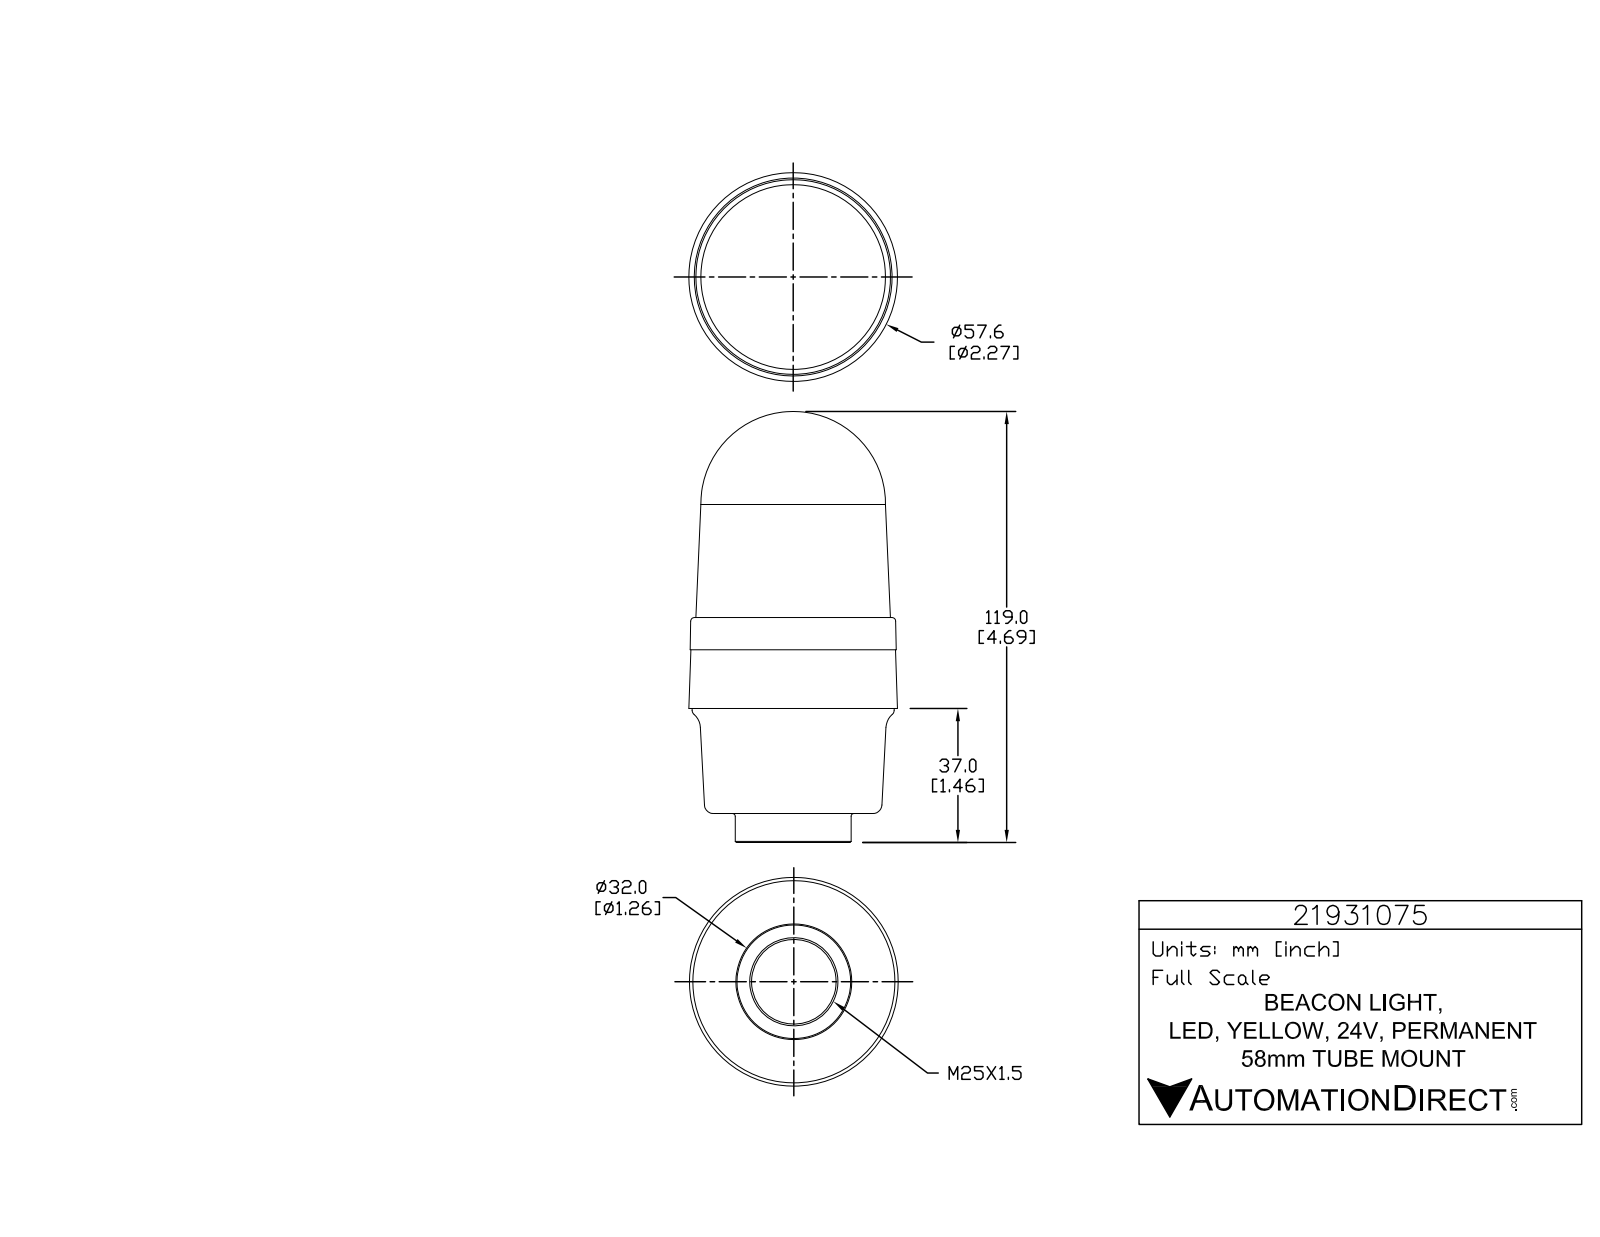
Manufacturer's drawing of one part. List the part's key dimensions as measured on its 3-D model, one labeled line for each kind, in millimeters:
Part name (STEP PRODUCT): 21931075
STEP written by: SolidWorks 2015 (AUTOMOTIVE_DESIGN)
Units: millimetres
Bodies: 1 solid, 791 faces (525 planar, 168 cylindrical, 98 other)
Overall size (bounding box): 119 × 57.6 × 57.6
Volume: 227 600 mm³ · Surface area: 21 970 mm²
Round holes (diameter × count): ⌀1 ×3, ⌀23.4 ×1
Round bosses / shafts (diameter × count): ⌀5.7 ×3, ⌀1.4 ×3, ⌀55.8 ×1, ⌀32 ×1
Partial cylindrical surfaces — rounded edges, fillets, slot ends (radius × count): R0.2 ×6, R0.2 ×6, R0.2 ×6, R3.3 ×6, R0.1 ×3, R0.1 ×3, R0.2 ×3, R0.2 ×3
Main face-to-face distances: 8, 29, 37, 25.1, 54.1, 62.1, 8.9, 16.2, 45.2, 53.2
